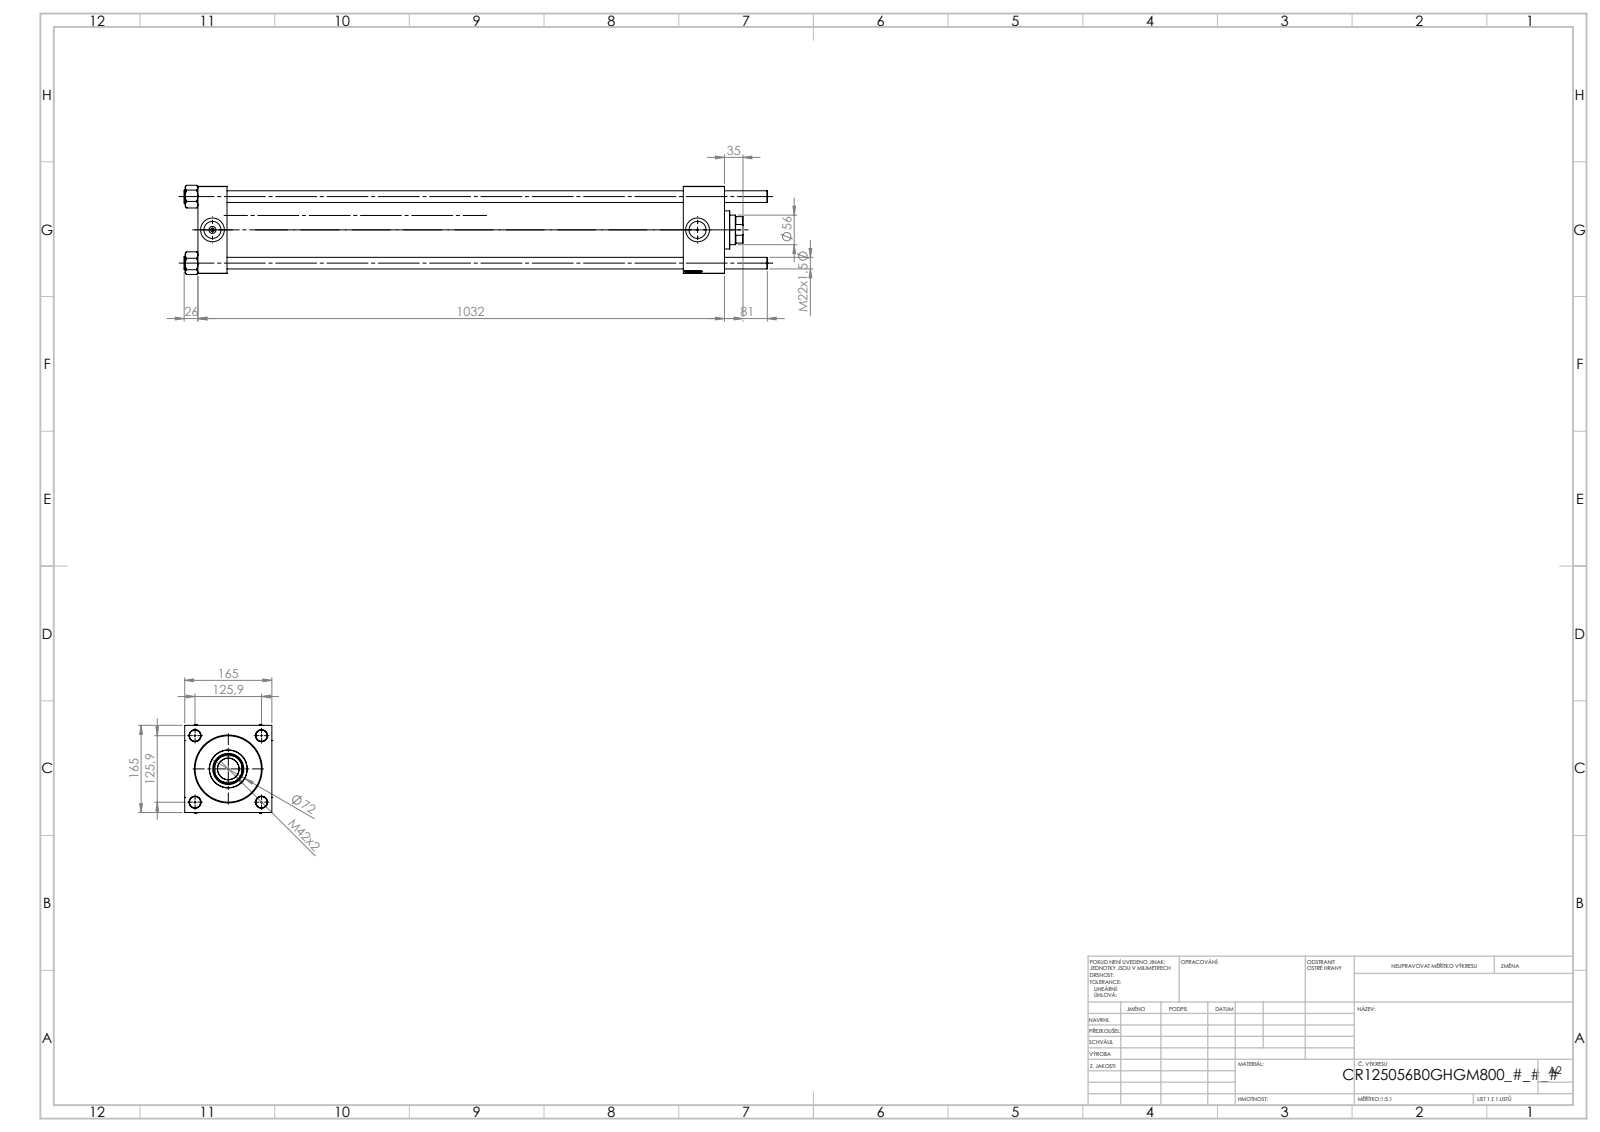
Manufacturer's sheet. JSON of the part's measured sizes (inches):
{"part_name": "NUT_M5_B; V215CR_VCP_B; V215CR_B_TYCINKA; V215CR_B-1 (+1 more)", "step_written_by": "SolidWorks 2019 (CONFIG_CONTROL_DESIGN)", "units": "inches", "bodies": {"solids": 11, "faces": 1206, "planar": 480, "cylindrical": 78, "other": 648}, "overall_size": [43.465, 6.653, 6.499], "volume_in3": 532.7, "surface_area_in2": 2370, "round_holes": [[0.866, 4], [0.276, 2], [1.269, 2], [1.772, 2], [1.594, 1], [2.205, 1], [2.323, 1], [3.78, 1], [4.921, 1], [4.941, 1]], "round_bosses_or_shafts": [[0.984, 4], [5.157, 1], [2.835, 1]], "partial_cylinders_radius": [[1.063, 1]], "face_to_face_distances": [6.496, 2.165, 39.252, 37.087, 36.181, 34.016, 3.071, 38.122, 35.957, 1.941], "hole_center_spacings": [3.505, 4.957, 7.01, 36.161]}
